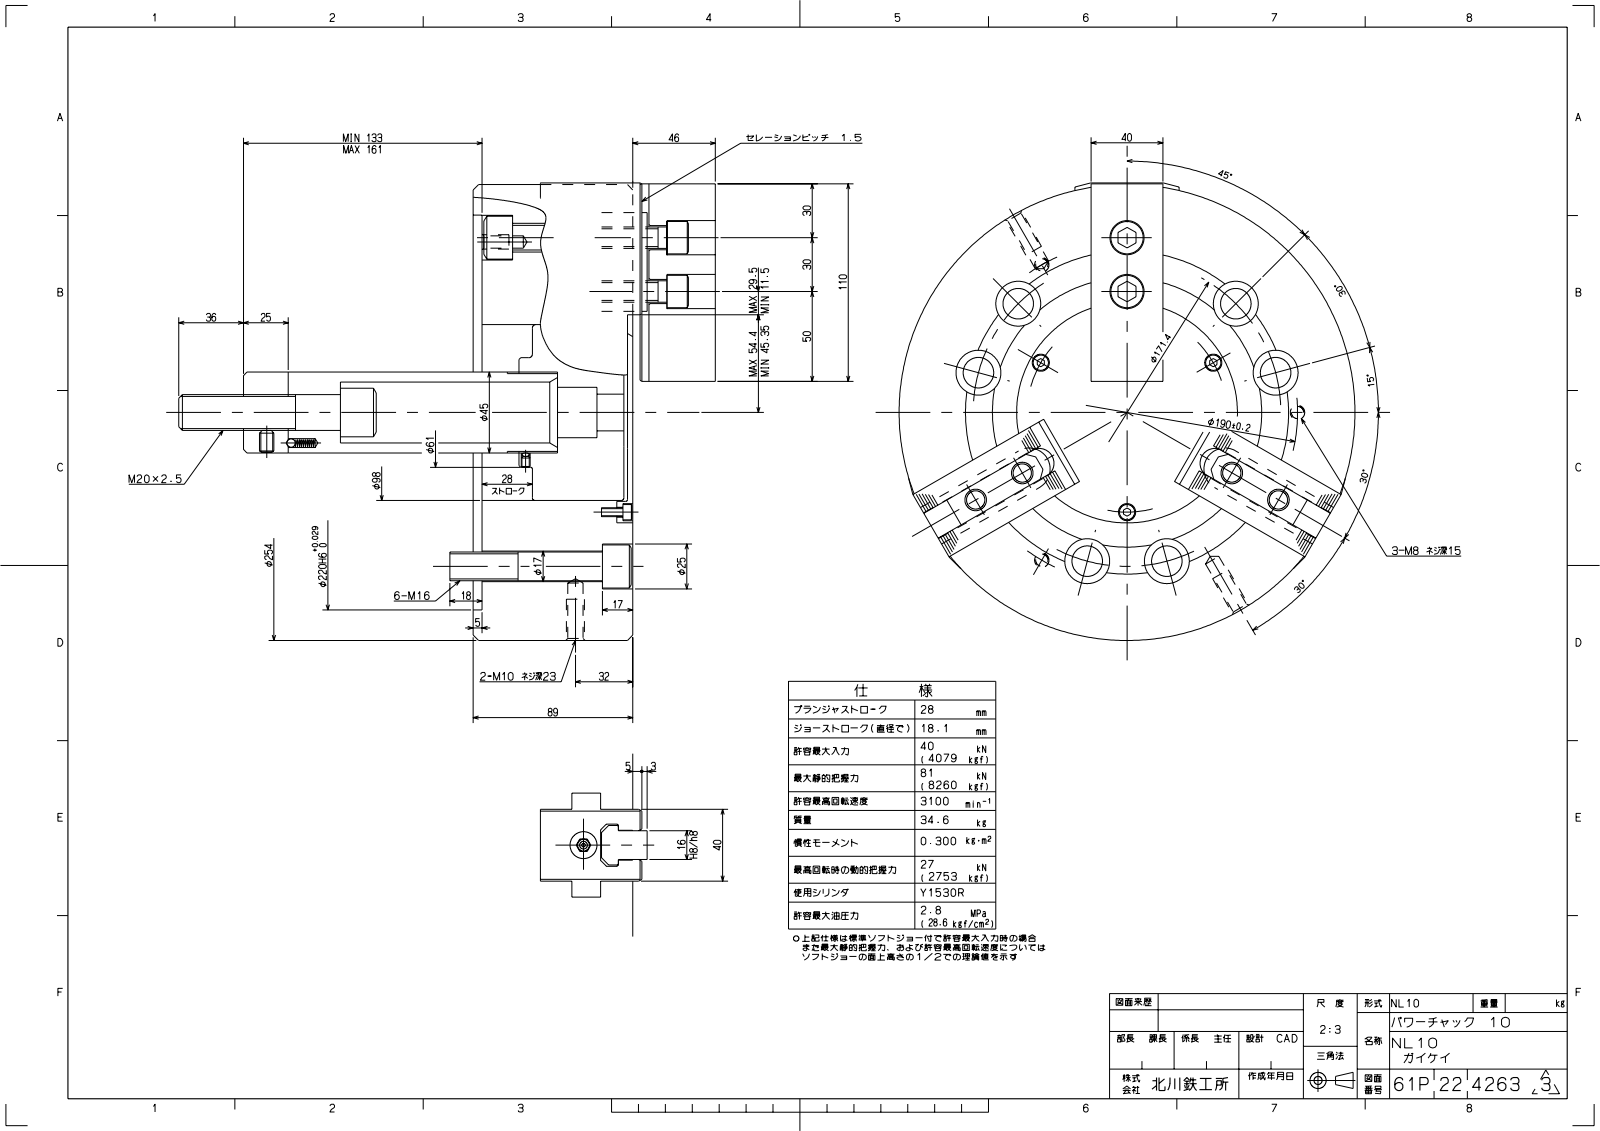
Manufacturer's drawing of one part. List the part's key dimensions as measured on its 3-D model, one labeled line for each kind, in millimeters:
Part name (STEP PRODUCT): NL10_ASSY
STEP written by: ST-DEVELOPER v16.7 (AUTOMOTIVE_DESIGN)
Units: millimetres
Bodies: 27 solids, 3082 faces (2832 planar, 144 cylindrical, 106 other)
Overall size (bounding box): 299.2 × 270.9 × 269.24
Volume: 4 507 000 mm³ · Surface area: 599 649 mm²
Round holes (diameter × count): ⌀5 ×10, ⌀17 ×9, ⌀25 ×9, ⌀12 ×6, ⌀13 ×6, ⌀19 ×6, ⌀22 ×6, ⌀8 ×4, ⌀4.2 ×3, ⌀5.5 ×3, ⌀6 ×3, ⌀6.8 ×3
Round bosses / shafts (diameter × count): ⌀18 ×6, ⌀24 ×3, ⌀8.5 ×3, ⌀254 ×1, ⌀98 ×1, ⌀61 ×1, ⌀45 ×1, ⌀27 ×1
Partial cylindrical surfaces — rounded edges, fillets, slot ends (radius × count): R4.5 ×6, R8.3 ×3, R11.75 ×3, R49.25 ×1, R61.5 ×1
Main face-to-face distances: 40, 84, 16, 9, 5, 28, 12, 18, 3, 66
Hole centre spacings: 113.54, 35.18, 66.67, 66.68, 73.91, 98.65, 155.92, 171.96
